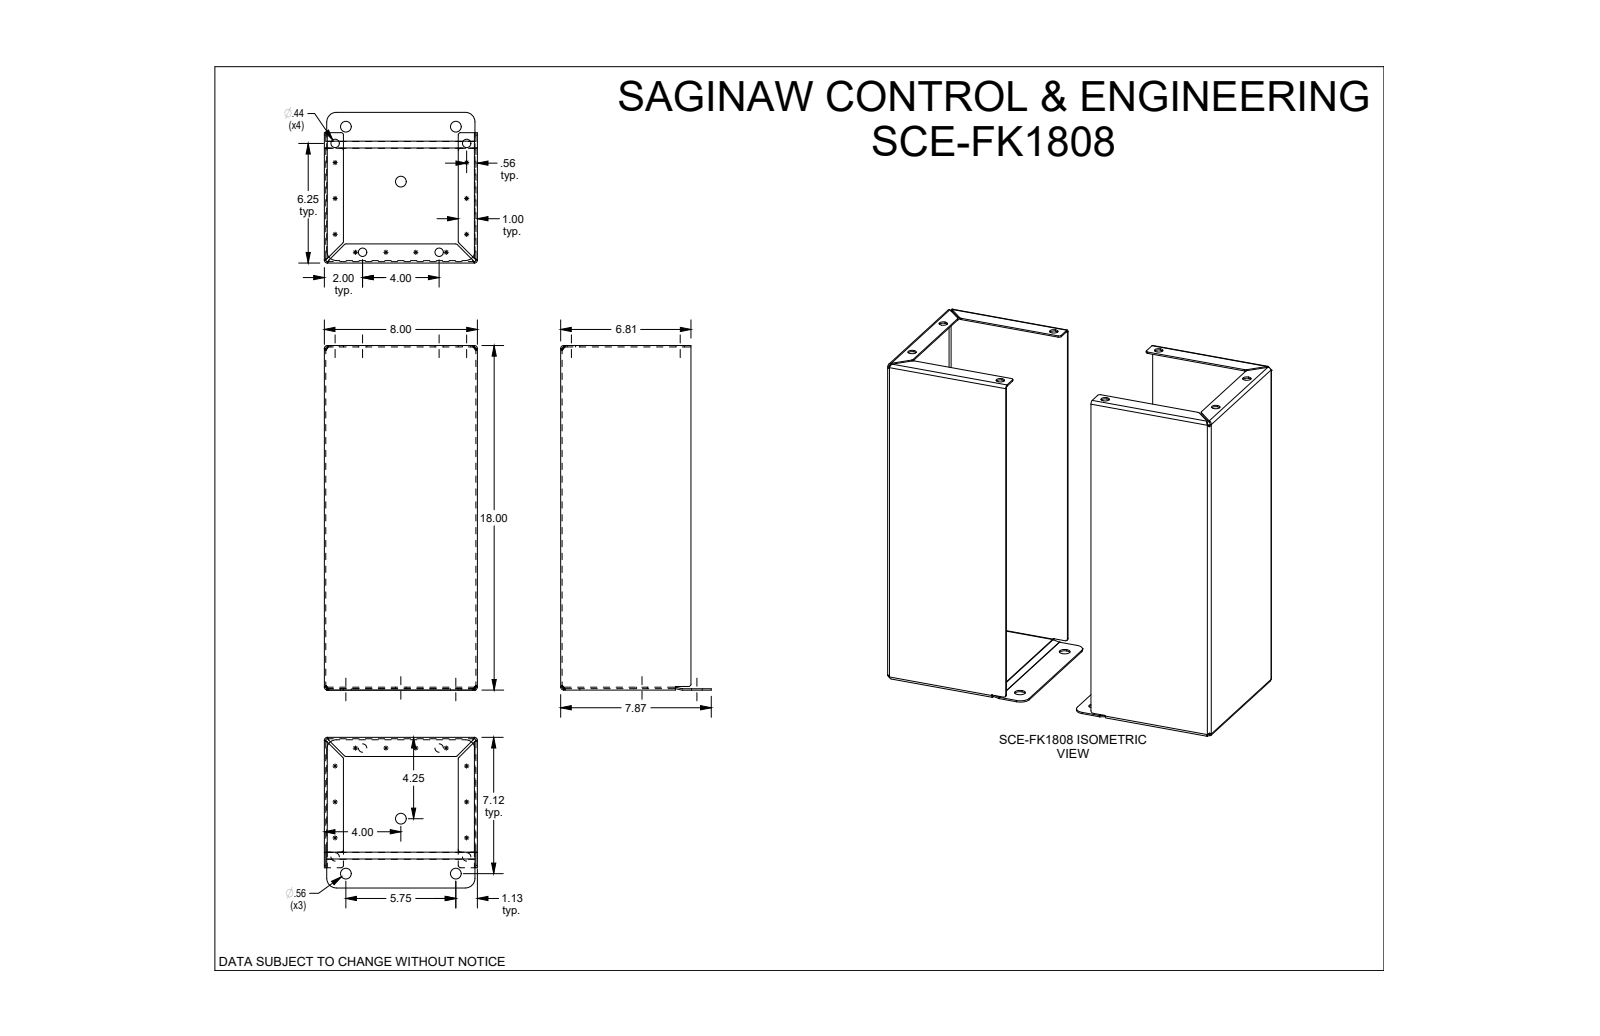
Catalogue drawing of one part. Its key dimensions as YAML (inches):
part_name: "SCE-FK1808"
step_written_by: "SolidWorks 2019 (CONFIG_CONTROL_DESIGN)"
units: inches
bodies: {solids: 4, faces: 222, planar: 96, cylindrical: 94, other: 32}
overall_size: [18.5, 18.005, 8]
volume: 71.19
surface_area: 1917
round_holes:
  - {diameter: 0.437, count: 8}
  - {diameter: 0.563, count: 6}
partial_cylinders:
  - {radius: 0.125, count: 18}
  - {radius: 0.08, count: 12}
  - {radius: 0.155, count: 12}
  - {radius: 0.5, count: 8}
  - {radius: 0.138, count: 4}
  - {radius: 0.02, count: 2}
  - {radius: 0.062, count: 2}
  - {radius: 0.063, count: 2}
face_to_face_distances: [0.075, 0.075, 7.925, 18.425, 8, 18.5, 18.35, 7.85, 7.925, 7.85]
hole_center_spacings: [3.976, 4.197, 5.158, 5.866, 6.618, 7.683, 7.869, 8.705]
